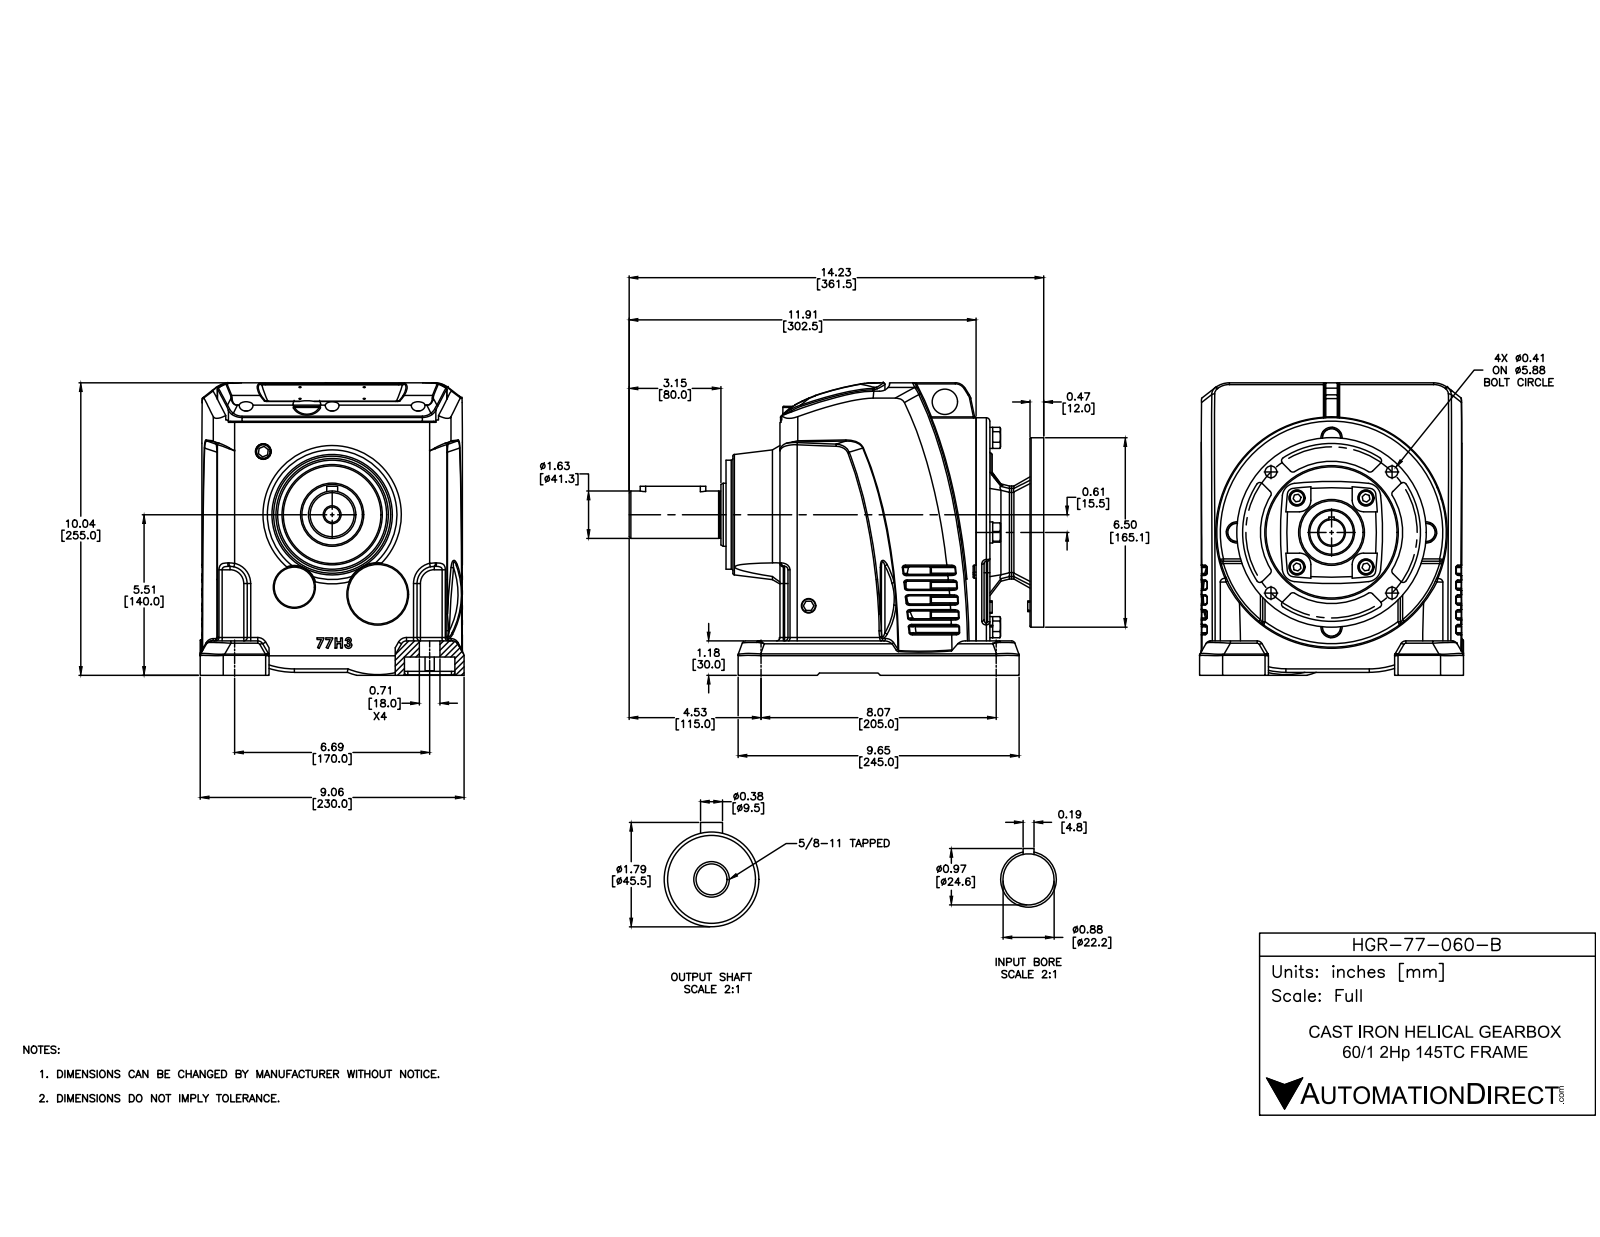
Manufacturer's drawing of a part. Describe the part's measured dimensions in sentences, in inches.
The part is named "HGR-77-060-B". Its 3-D file was written by "SolidWorks 2015 (CONFIG_CONTROL_DESIGN)". It is 30 solids with 1200 faces: 383 planar, 313 cylindrical and 504 other. Overall it measures 14.232 by 10.039 by 9.055 inches. Its volume is 553.2 cubic inches and its surface area 938.6 square inches. Round holes: 6 of diameter 0.472, 4 of diameter 0.079, 4 of diameter 0.406, 4 of diameter 0.551, 4 of diameter 0.709, 1 of diameter 0.531, 1 of diameter 0.866, 1 of diameter 0.875, 1 of diameter 0.945, 1 of diameter 1.575, 1 of diameter 2.165, 1 of diameter 4.5. Round bosses or shafts: 9 of diameter 0.512, 4 of diameter 0.724, 3 of diameter 0.394, 1 of diameter 7.874, 1 of diameter 6.5, 1 of diameter 3.74, 1 of diameter 3.346, 1 of diameter 2.165. Partial cylindrical surfaces (rounded edges, fillets, slot ends): 58 of radius 0.118, 33 of radius 0.039, 8 of radius 0.394, 6 of radius 0.079, 5 of radius 0.062, 4 of radius 0.197, 4 of radius 0.315, 4 of radius 0.591. The main face-to-face distances are 8.583, 0.039, 0.472, 1.85, 6.732, 0.276, 1.378, 8.858, 8.543, 7.205. The hole center spacings are 3.381, 1.265, 1.673, 2.366, 2.937, 4.154, 4.611, 6.693.
